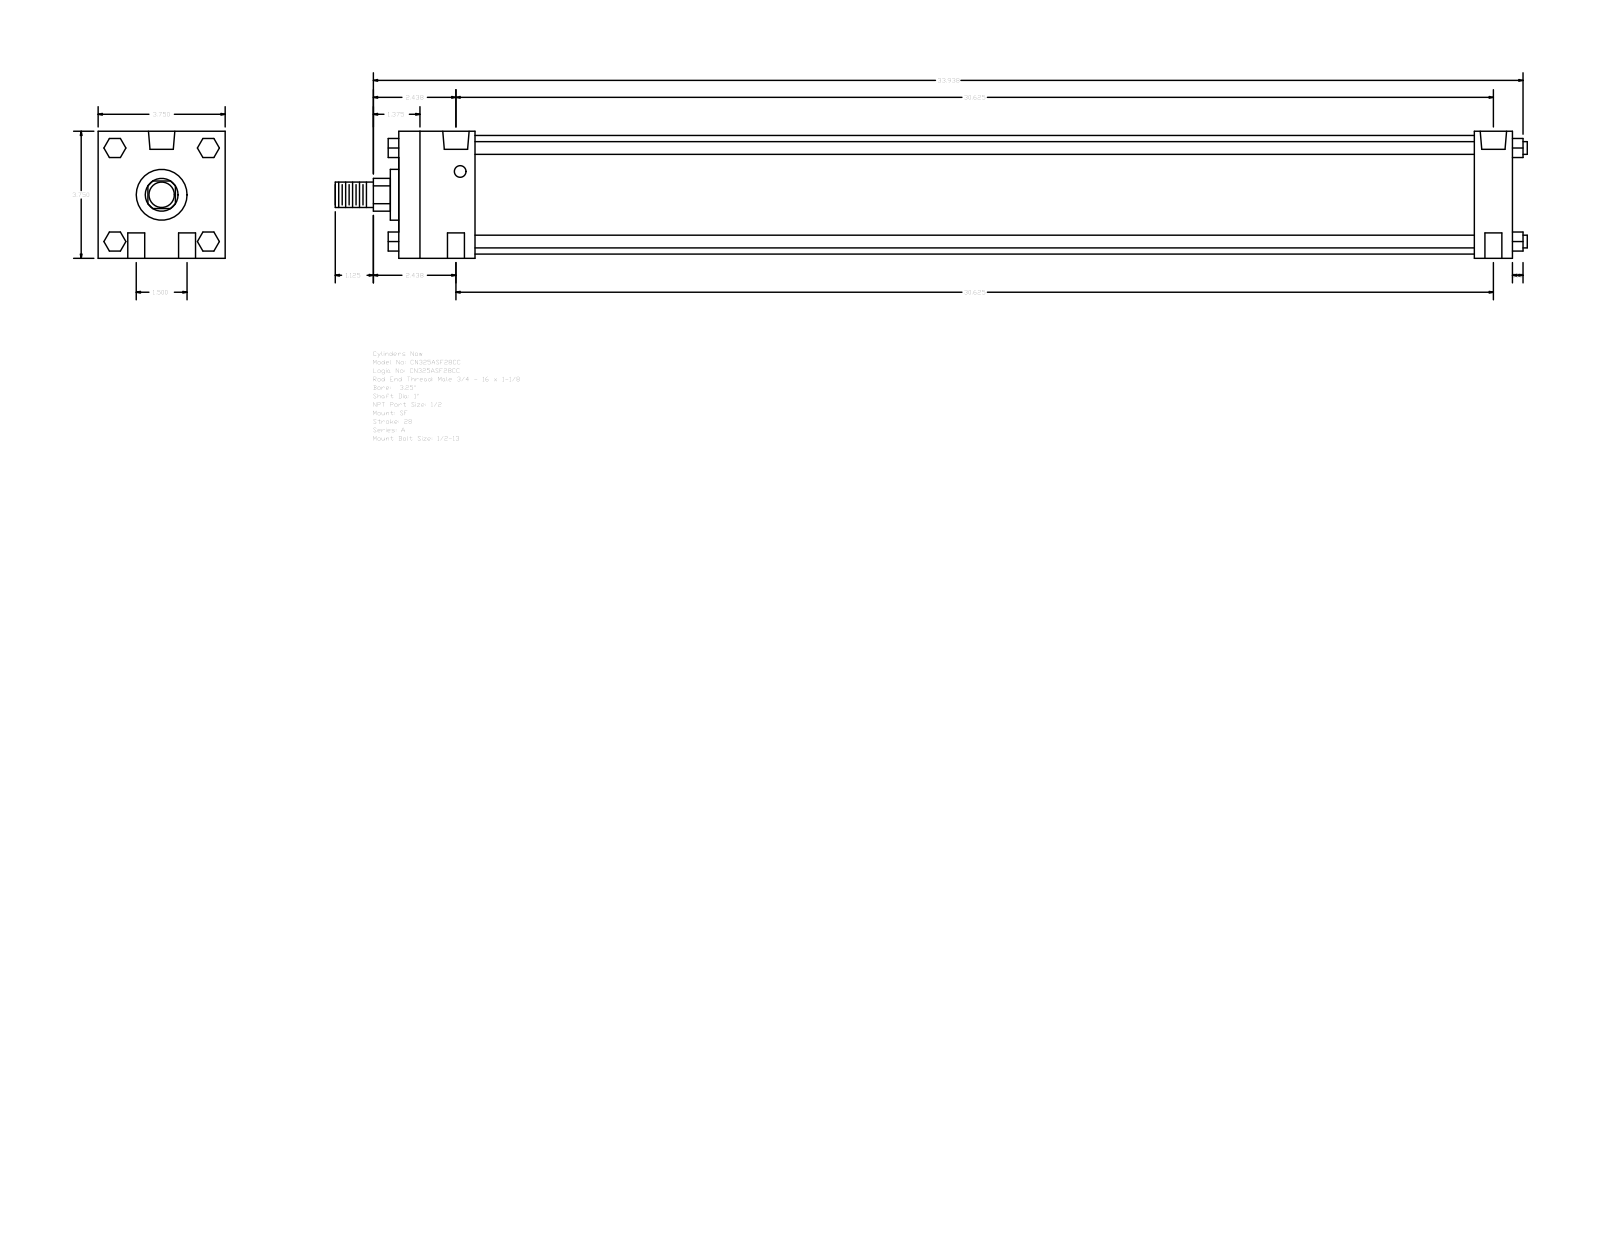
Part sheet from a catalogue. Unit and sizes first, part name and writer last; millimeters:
Units: millimetres
Overall size (bounding box): 893.76 × 95.25 × 95.25
Round holes (diameter × count): ⌀12.7 ×4, ⌀8.73 ×2, ⌀19.77 ×2
Round bosses / shafts (diameter × count): ⌀9.53 ×4, ⌀88.9 ×1, ⌀38.1 ×1, ⌀25.4 ×1, ⌀19.05 ×1
Partial cylindrical surfaces — rounded edges, fillets, slot ends (radius × count): R12.29 ×1
Main face-to-face distances: 95.24, 835.03, 806.45, 28.58, 57.15, 749.3, 777.88, 14.28, 35.05, 60.71
Hole centre spacings: 19.05, 778.11, 777.88, 38.1, 778.81, 771.52
Bodies: 0 solids, 124 faces (94 planar, 30 cylindrical, 0 other)
Part name (STEP PRODUCT): A_SF__0325_1
STEP written by: GSSL Pune (CONFIG_CONTROL_DESIGN)
